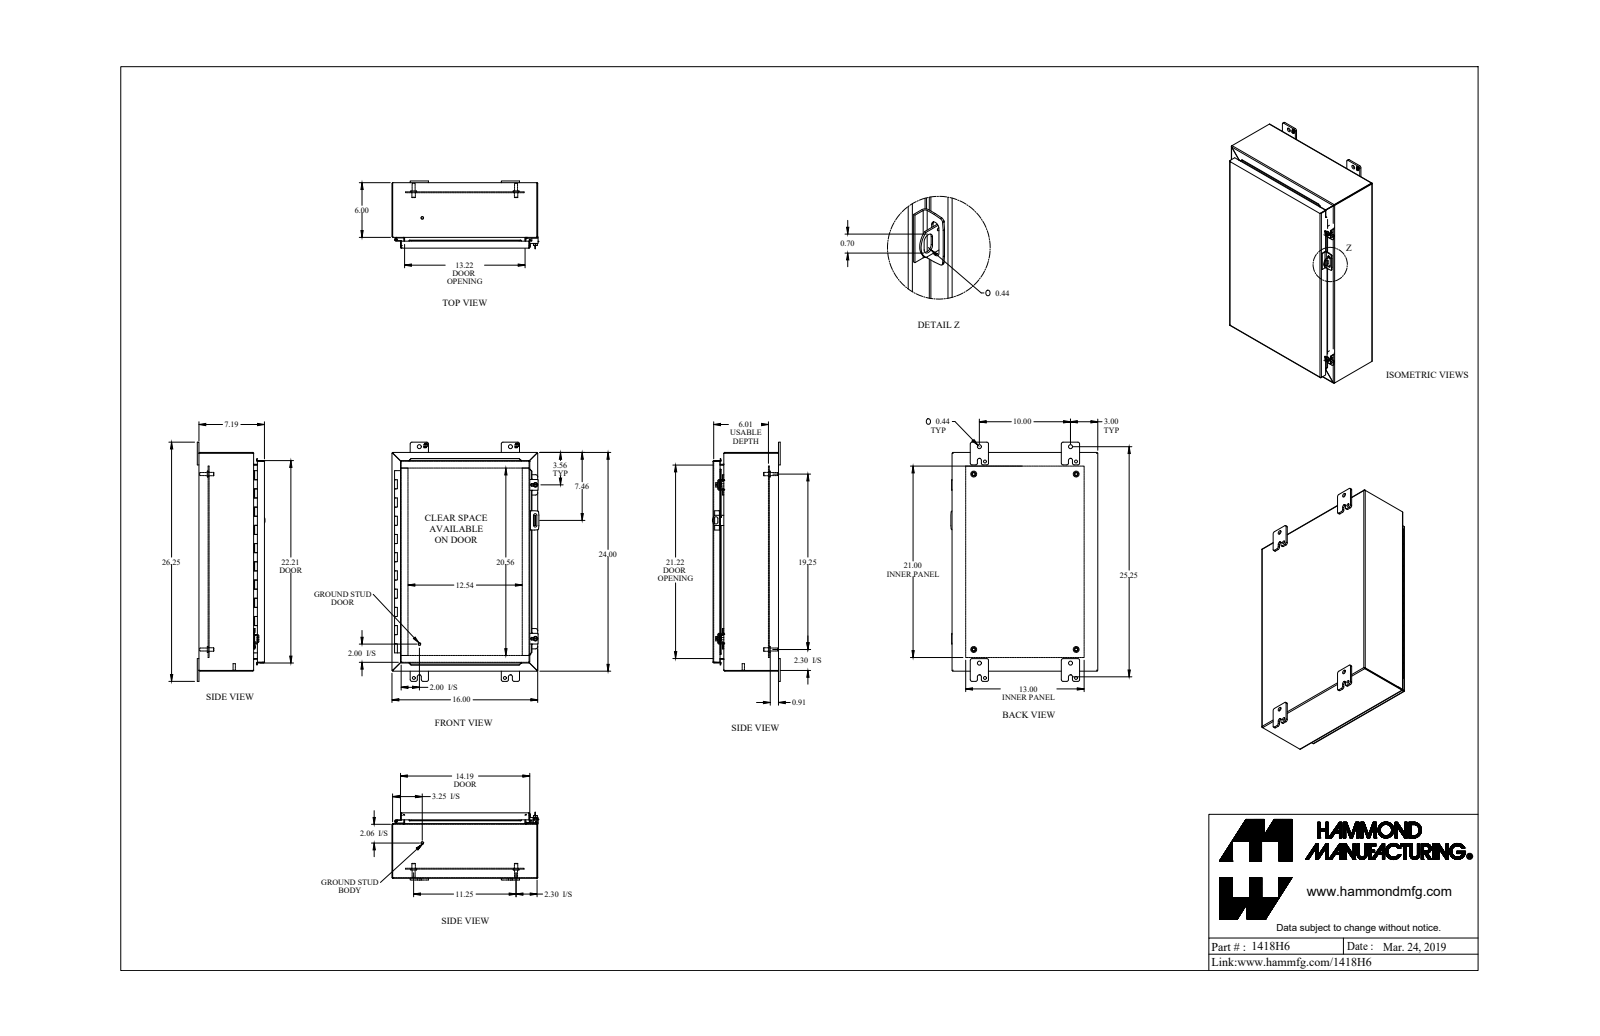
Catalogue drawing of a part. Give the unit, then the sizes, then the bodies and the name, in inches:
Units: inches
Overall size (bounding box): 26.25 × 16.125 × 7.437
Round holes (diameter × count): ⌀0.313 ×4, ⌀0.437 ×4, ⌀0.5 ×4, ⌀0.213 ×2, ⌀0.265 ×2, ⌀0.307 ×2, ⌀0.375 ×2, ⌀0.445 ×2, ⌀0.125 ×1, ⌀0.187 ×1
Round bosses / shafts (diameter × count): ⌀0.65 ×4, ⌀0.375 ×4, ⌀0.33 ×4, ⌀1 ×2, ⌀0.5 ×2, ⌀0.39 ×2, ⌀0.281 ×2, ⌀0.25 ×2
Partial cylindrical surfaces — rounded edges, fillets, slot ends (radius × count): R0.188 ×26, R0.036 ×20, R0.108 ×20, R0.048 ×13, R0.143 ×13, R0.007 ×8, R0.045 ×8, R0.079 ×8
Main face-to-face distances: 0.072, 7.113, 7.041, 0.937, 7.185, 1.009, 0.095, 15.928, 6.081, 6.009
Hole centre spacings: 10, 1.735, 23.75, 25.769, 1.625, 3.065, 10.492, 10.73
Volume: 146.5 in³ · Surface area: 3 794 in²
Bodies: 38 solids, 1002 faces (689 planar, 259 cylindrical, 54 other)
Part name (STEP PRODUCT): 1418H6
STEP written by: SolidWorks 2019 (AUTOMOTIVE_DESIGN)
